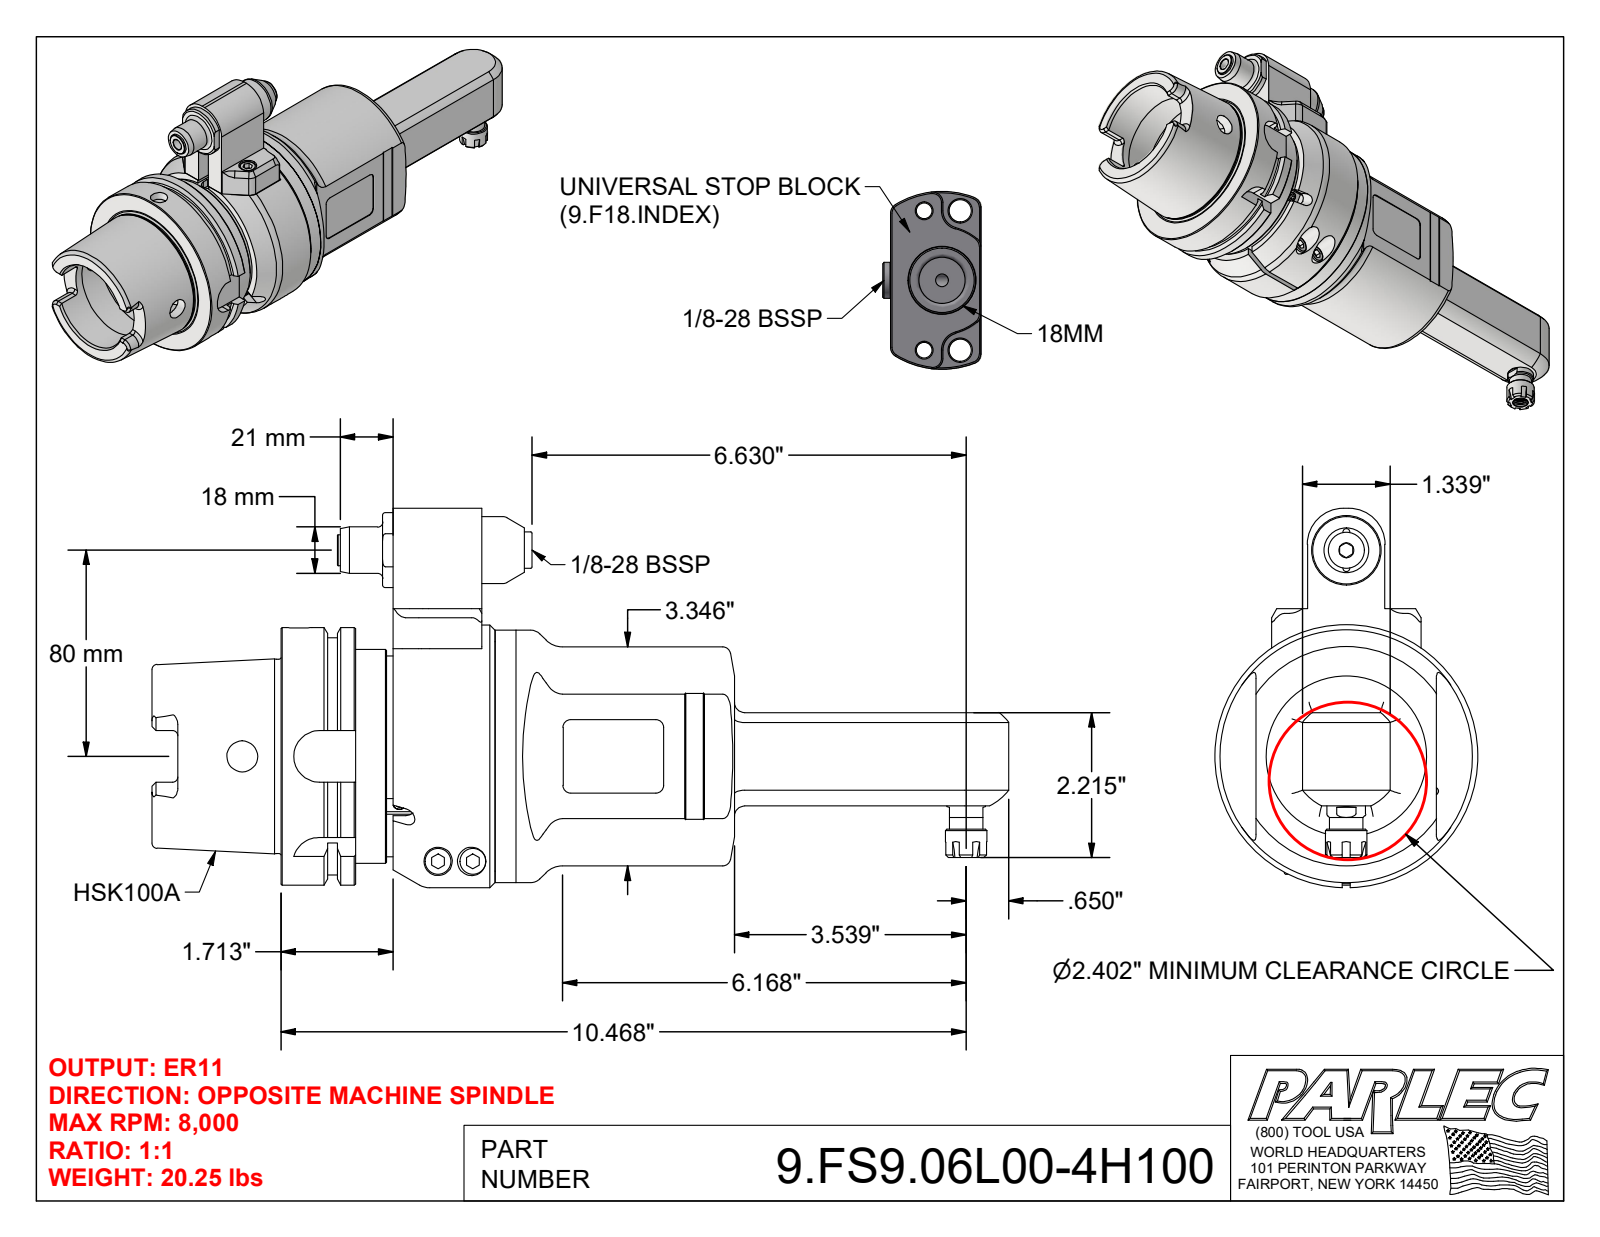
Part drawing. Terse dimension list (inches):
name: 9.FS9.06L00-4H100; 9_FS9_06L00; 9_GA1_518_2 (Type 1, H100A, 80mm)
written by: Autodesk Inventor 2022 (AUTOMOTIVE_DESIGN)
unit: in
bodies: 5 solids, 637 faces (291 planar, 179 cylindrical, 167 other)
size: 13.086 × 5.796 × 4.016
volume: 80.35 in³; area: 289.3 in²
holes: 17× ⌀0.335, 6× ⌀0.102, 5× ⌀0.197, 4× ⌀0.402, 2× ⌀0.264, 2× ⌀0.409, 2× ⌀0.433, 2× ⌀0.472, 1× ⌀0.098, 1× ⌀0.118, 1× ⌀0.165, 1× ⌀0.236
bosses: 8× ⌀0.394, 4× ⌀0.236, 2× ⌀0.709, 2× ⌀0.315, 2× ⌀0.098, 1× ⌀4.016, 1× ⌀3.937, 1× ⌀3.858
rounds: 14× R0.079, 9× R0.157, 6× R1.181, 4× R0.118, 4× R0.192, 4× R0.394, 2× R0.02, 2× R0.039
face distances: 2.047, 1.26, 1.22, 0.709, 1.555, 0.039, 0.65, 1.142, 1.063, 0.335
hole spacings: 1.486, 2.102, 0.759, 1.058, 1.077, 1.145, 1.496, 1.852
